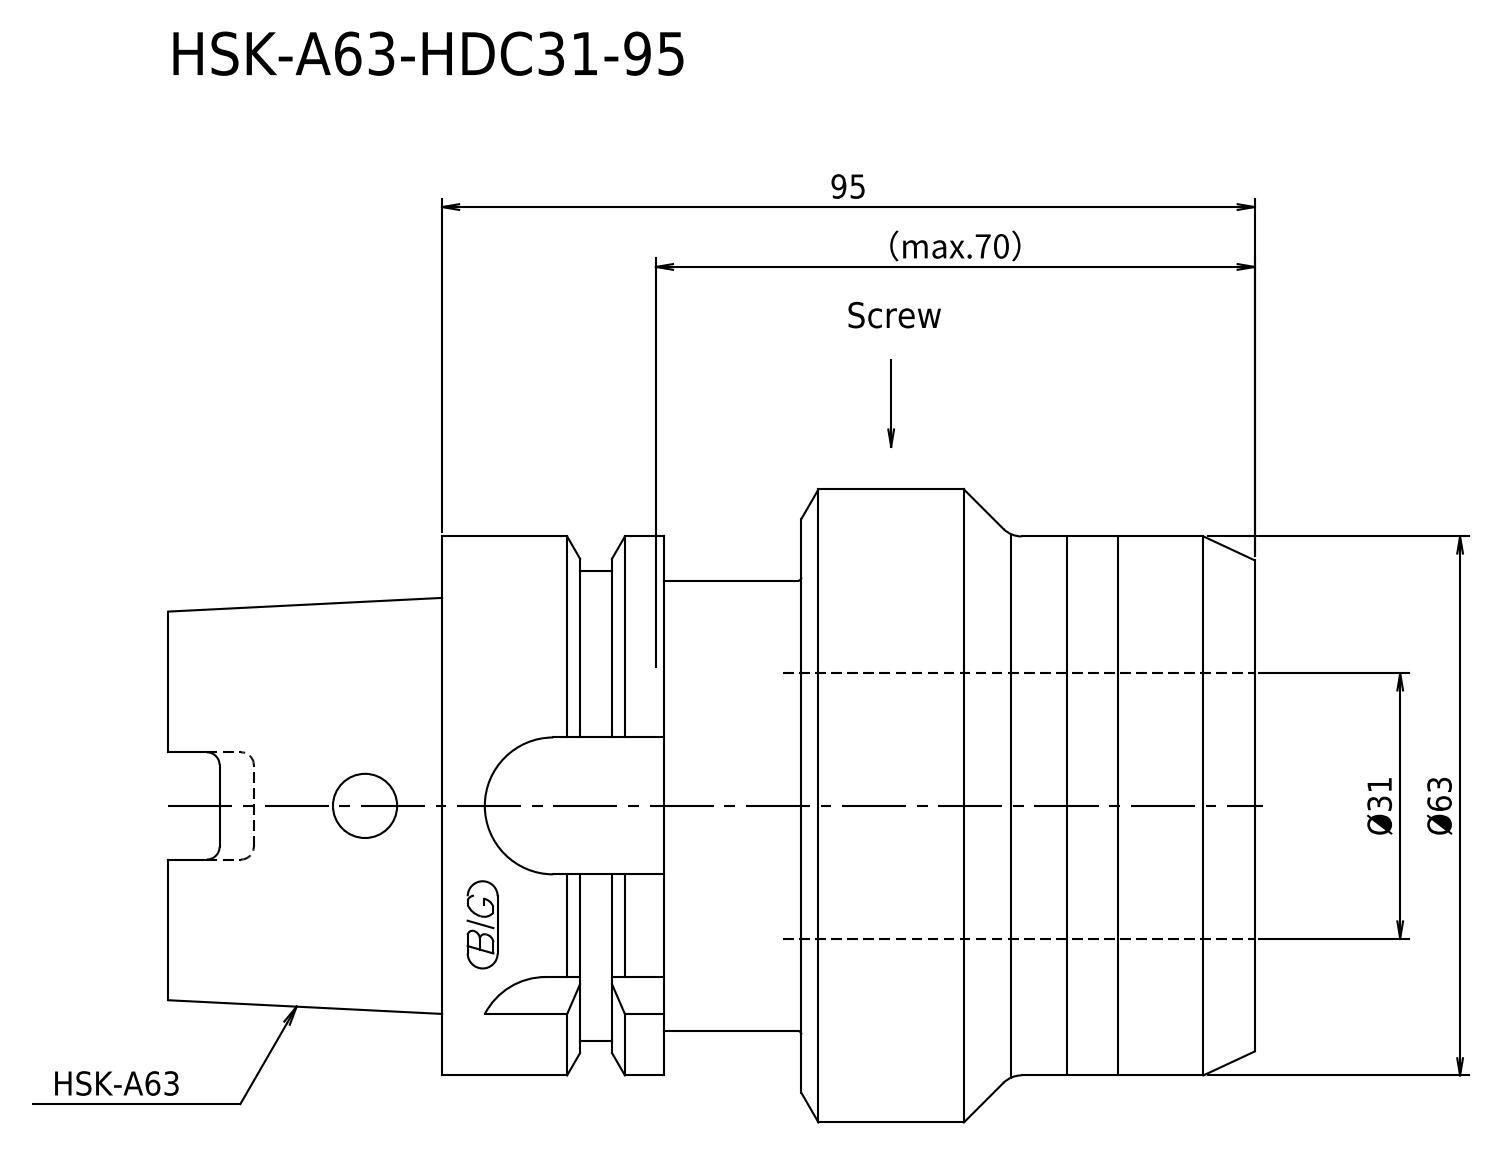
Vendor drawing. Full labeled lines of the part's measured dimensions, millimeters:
STEP written by: Kubotek KeyCreator 2011 V10.0.2 (22737) (automotive_design)
Units: millimetres
Bodies: 1 solid, 19 faces (7 planar, 6 cylindrical, 6 other)
Overall size (bounding box): 127 × 74 × 74
Volume: 356 372 mm³ · Surface area: 33 461 mm²
Round bosses / shafts (diameter × count): ⌀74 ×1, ⌀63 ×1, ⌀55 ×1, ⌀52.6 ×1
Main face-to-face distances: 127, 53, 74, 95, 42, 32, 69, 16, 26, 58
